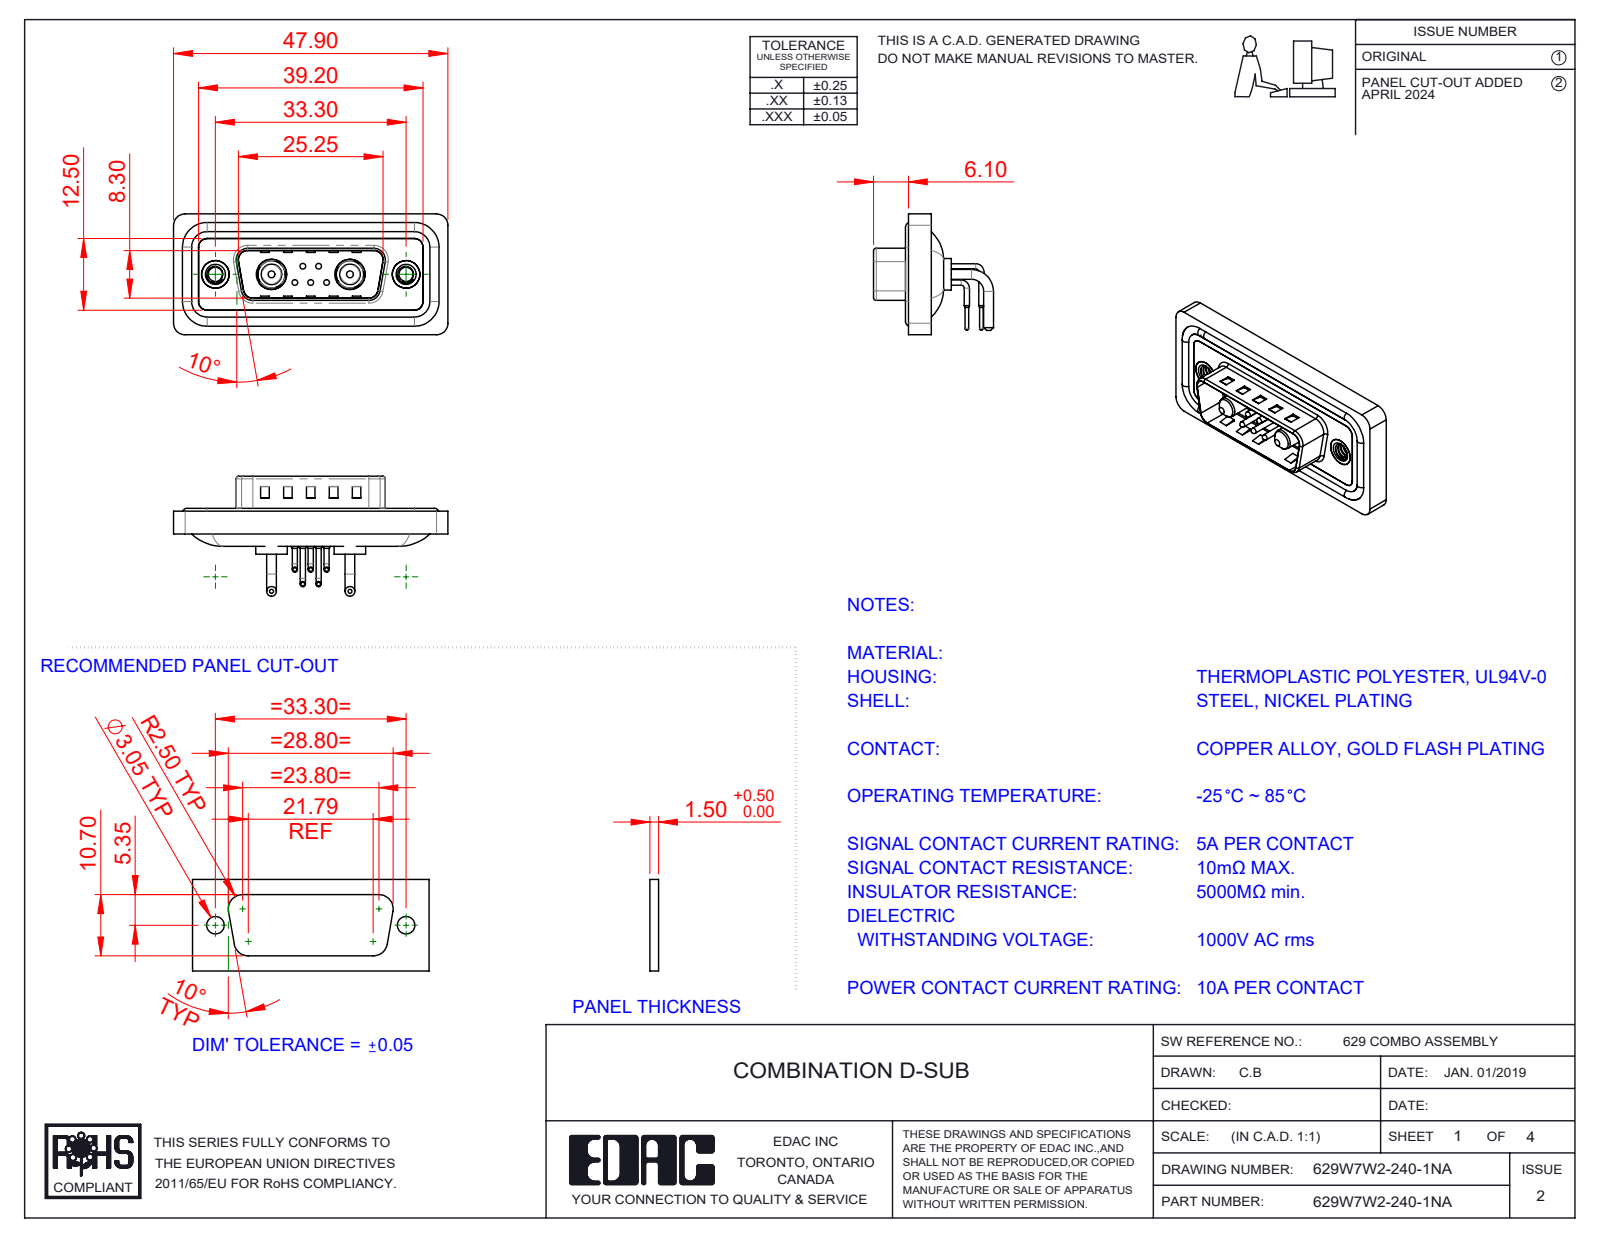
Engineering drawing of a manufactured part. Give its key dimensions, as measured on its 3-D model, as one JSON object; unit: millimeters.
{"part_name": "629Combo Shell Front_15 Contacts; 629Combo Waterproof Housing_15 Contacts; 629Combo Contact Row 1; 629Combo Threaded Rivet_A (+5 more)", "step_written_by": "SolidWorks 2023 (CONFIG_CONTROL_DESIGN)", "units": "millimeters", "bodies": {"solids": 16, "faces": 1077, "planar": 517, "cylindrical": 404, "other": 156}, "overall_size": [47.9, 21.1, 20.95], "volume_mm3": 5568, "surface_area_mm2": 9043, "round_holes": [[0.75, 5], [1.6, 5], [2, 5], [2.5, 2], [4, 2], [4.8, 2], [4.85, 2], [5, 2], [5.3, 2]], "round_bosses_or_shafts": [[0.9, 10], [1.5, 5], [1, 5], [0.65, 5], [1.7, 4], [1.6, 4], [5.5, 2], [5.2, 2]], "partial_cylinders_radius": [[2, 20], [1.5, 18], [0.5, 8], [1.6, 8], [1.01, 5], [0.25, 4], [0.6, 4], [0.65, 4]], "face_to_face_distances": [0.4, 2.9, 0.8, 1.1, 2.1, 1.6, 2.5, 3.1, 4.5, 4.1], "hole_center_spacings": [3.16, 2.77, 9.8, 23.5, 4.31, 4.33, 5.03, 5.04]}
